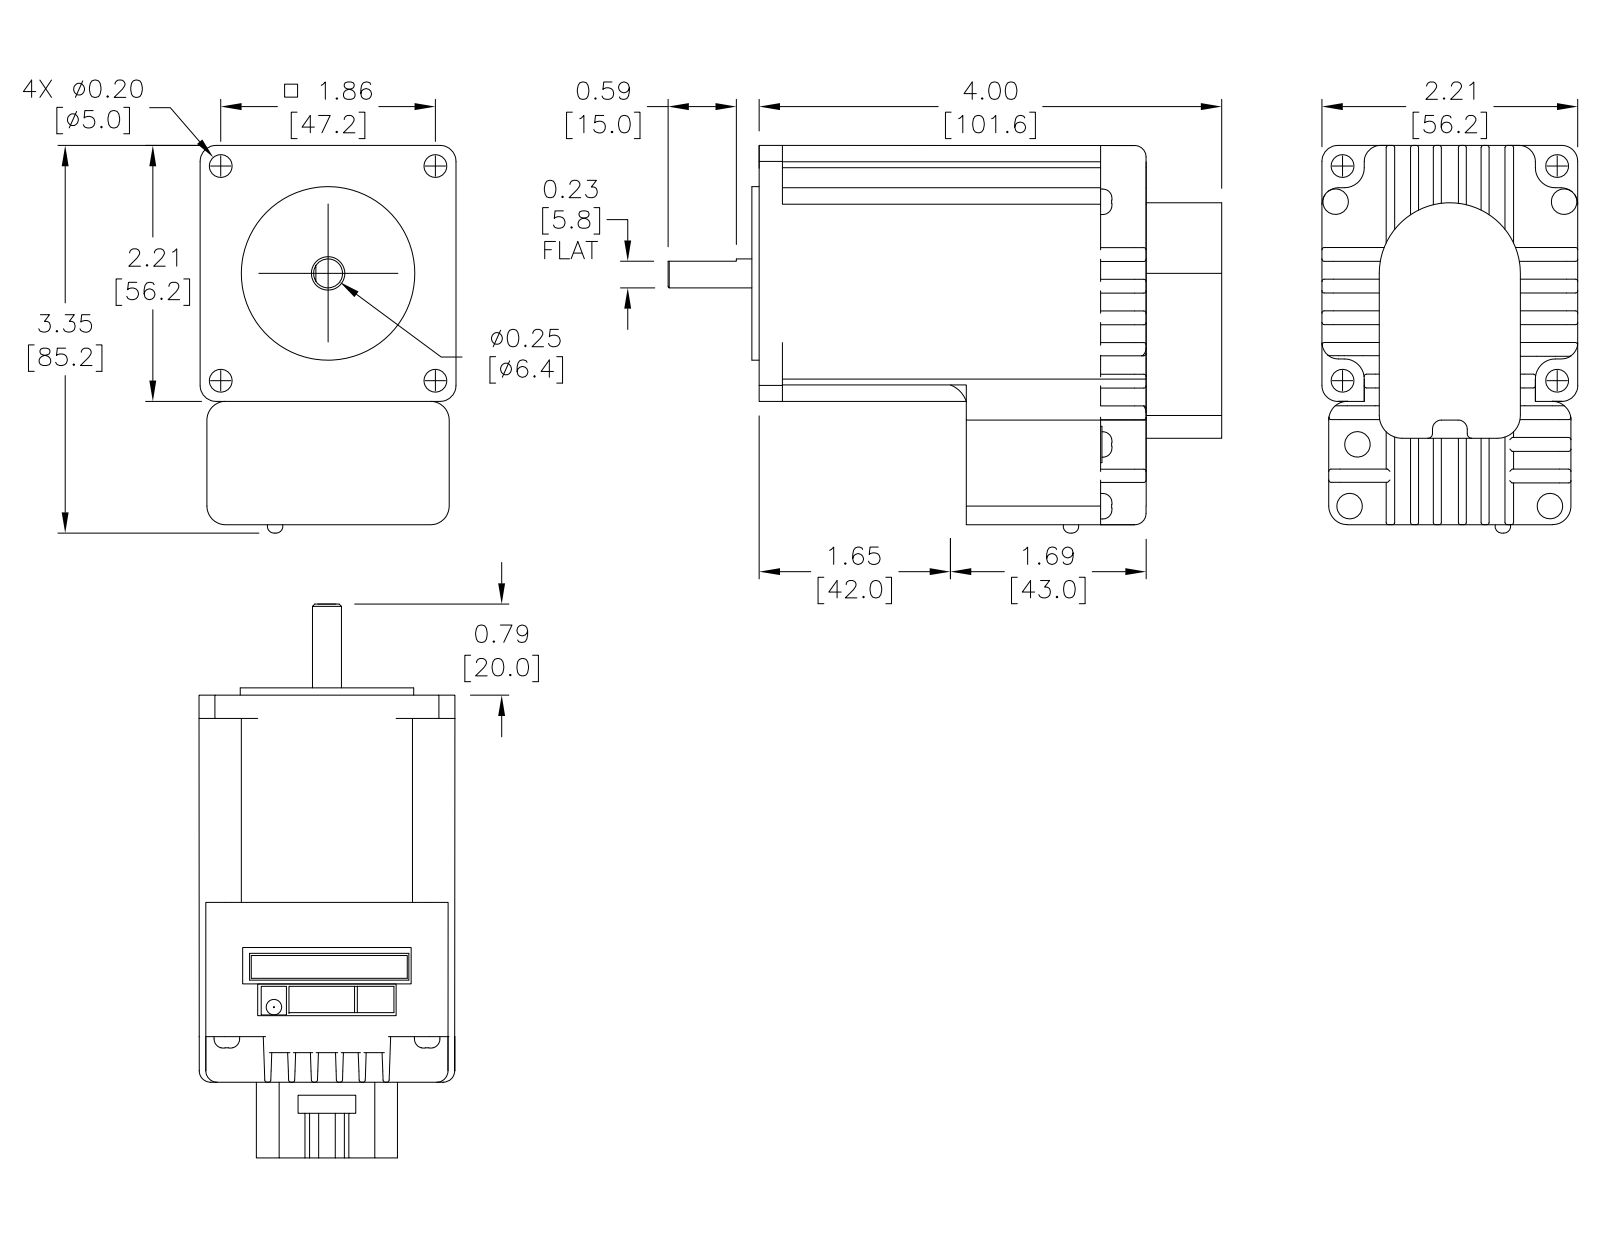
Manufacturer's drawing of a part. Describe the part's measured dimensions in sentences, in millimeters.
The part is named "STP-MTRD-23042E". Its 3-D file was written by "SolidWorks 2017 (AUTOMOTIVE_DESIGN)". It is 1 solid with 712 faces: 331 planar, 260 cylindrical and 121 other. Overall it measures 121.6 by 84.8 by 56.2 millimeters. Its volume is 297 960 cubic millimeters and its surface area 46 031 square millimeters. Round holes: 4 of diameter 5, 1 of diameter 2, 1 of diameter 7.35. Round bosses or shafts: 5 of diameter 5.6, 4 of diameter 5.5, 1 of diameter 38.1, 1 of diameter 8, 1 of diameter 6.35. Partial cylindrical surfaces (rounded edges, fillets, slot ends): 87 of radius 0.5, 10 of radius 2.5, 8 of radius 3.6, 5 of radius 0.68, 5 of radius 10.96, 4 of radius 2, 4 of radius 3.2, 4 of radius 3.5. The main face-to-face distances are 56.2, 4.99, 10.49, 10, 5.25, 15.74, 20.73, 10.24, 85, 23.1. The hole center spacings are 33.33, 47.14, 66.67.
